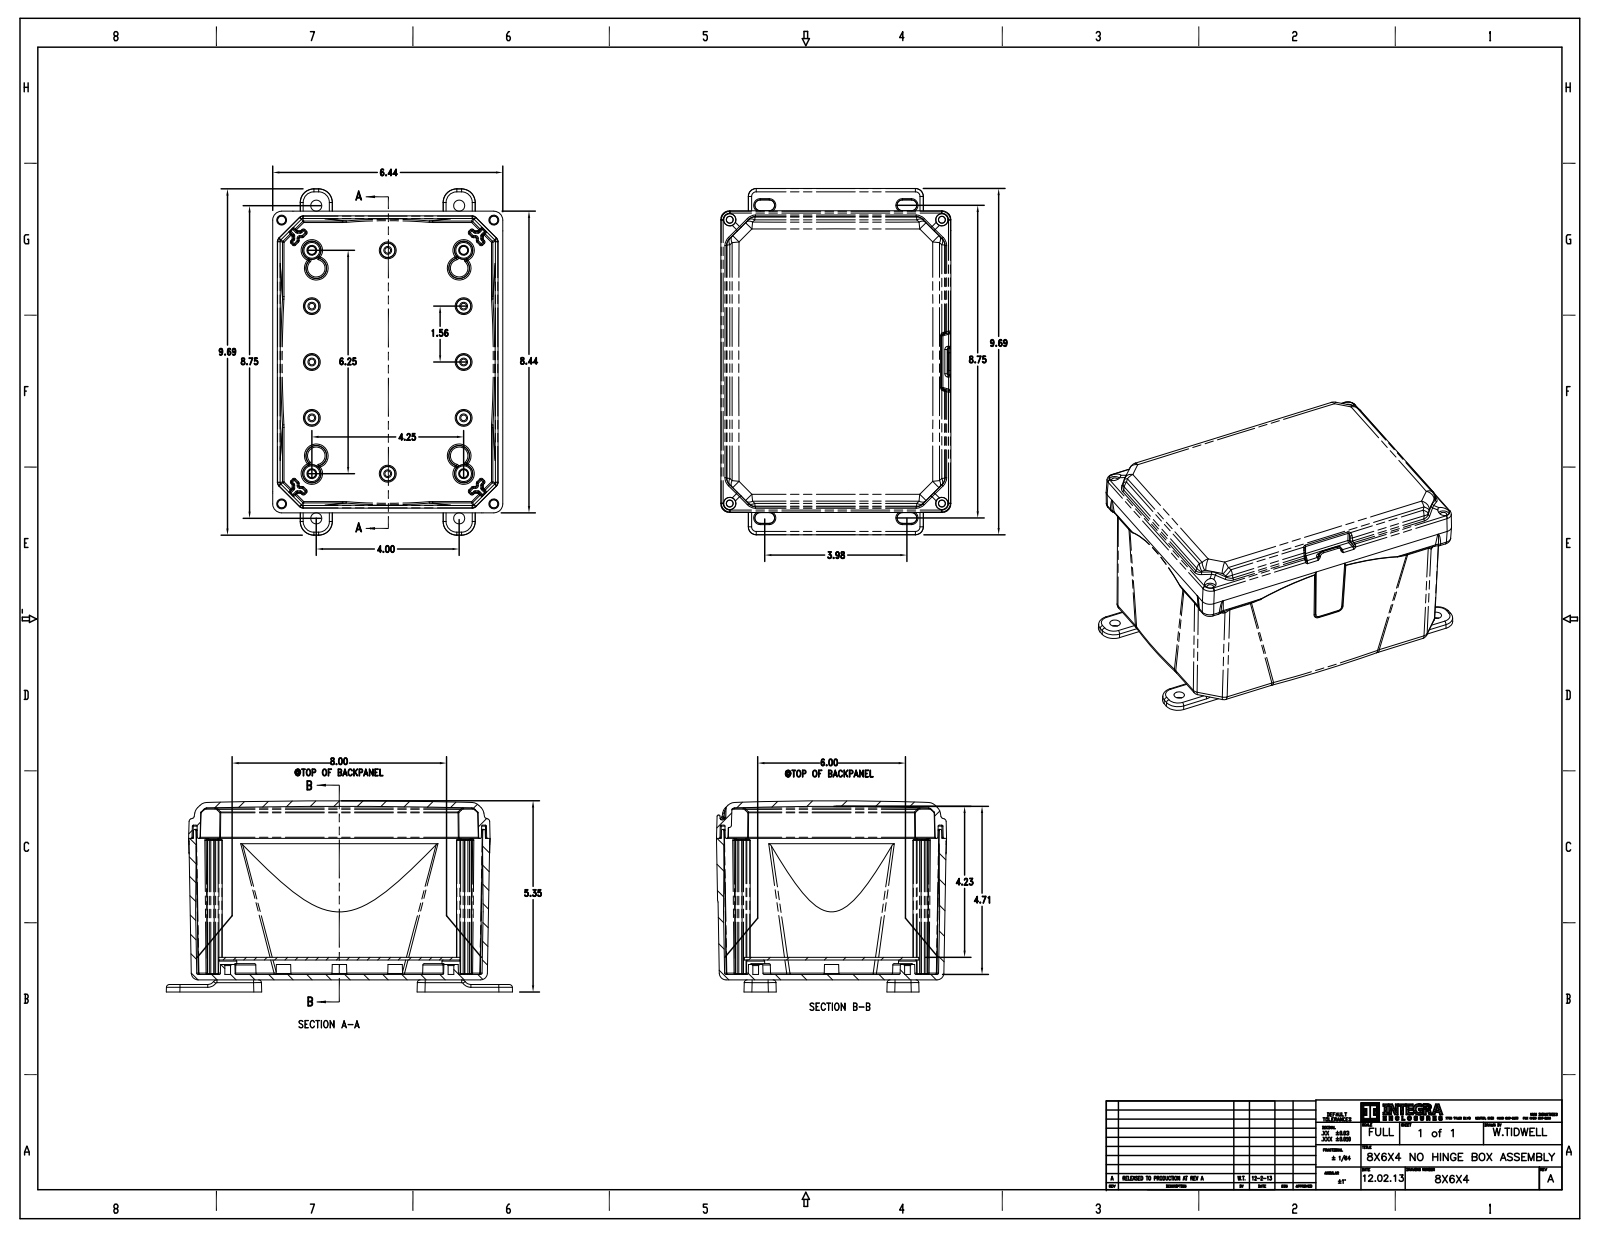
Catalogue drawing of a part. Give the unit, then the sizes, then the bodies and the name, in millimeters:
Units: millimetres
Overall size (bounding box): 246.1 × 163.6 × 135.9
Round holes (diameter × count): ⌀4.1 ×8, ⌀7.1 ×4
Partial cylindrical surfaces — rounded edges, fillets, slot ends (radius × count): R0.8 ×318, R0.6 ×64, R0.5 ×61, R2.3 ×44, R1.5 ×37, R2 ×31, R6.4 ×28, R1 ×24
Main face-to-face distances: 3.8, 14.1, 10.3, 16, 12.2, 1.9, 8.1, 3, 8.6, 5.7
Hole centre spacings: 108, 39.7, 39.7, 54, 67, 79.4, 96, 115
Volume: 745 600 mm³ · Surface area: 430 800 mm²
Bodies: 5 solids, 2606 faces (493 planar, 963 cylindrical, 1150 other)
Part name (STEP PRODUCT): 806400; 806440; 8X6X4-BACK-PANEL; 6INCH-MOUNTING-FLANGE (+1 more)
STEP written by: PRO/ENGINEER BY PARAMETRIC TECHNOLOGY CORPORATION, 2004110 (CONFIG_CONTROL_DESIGN)
